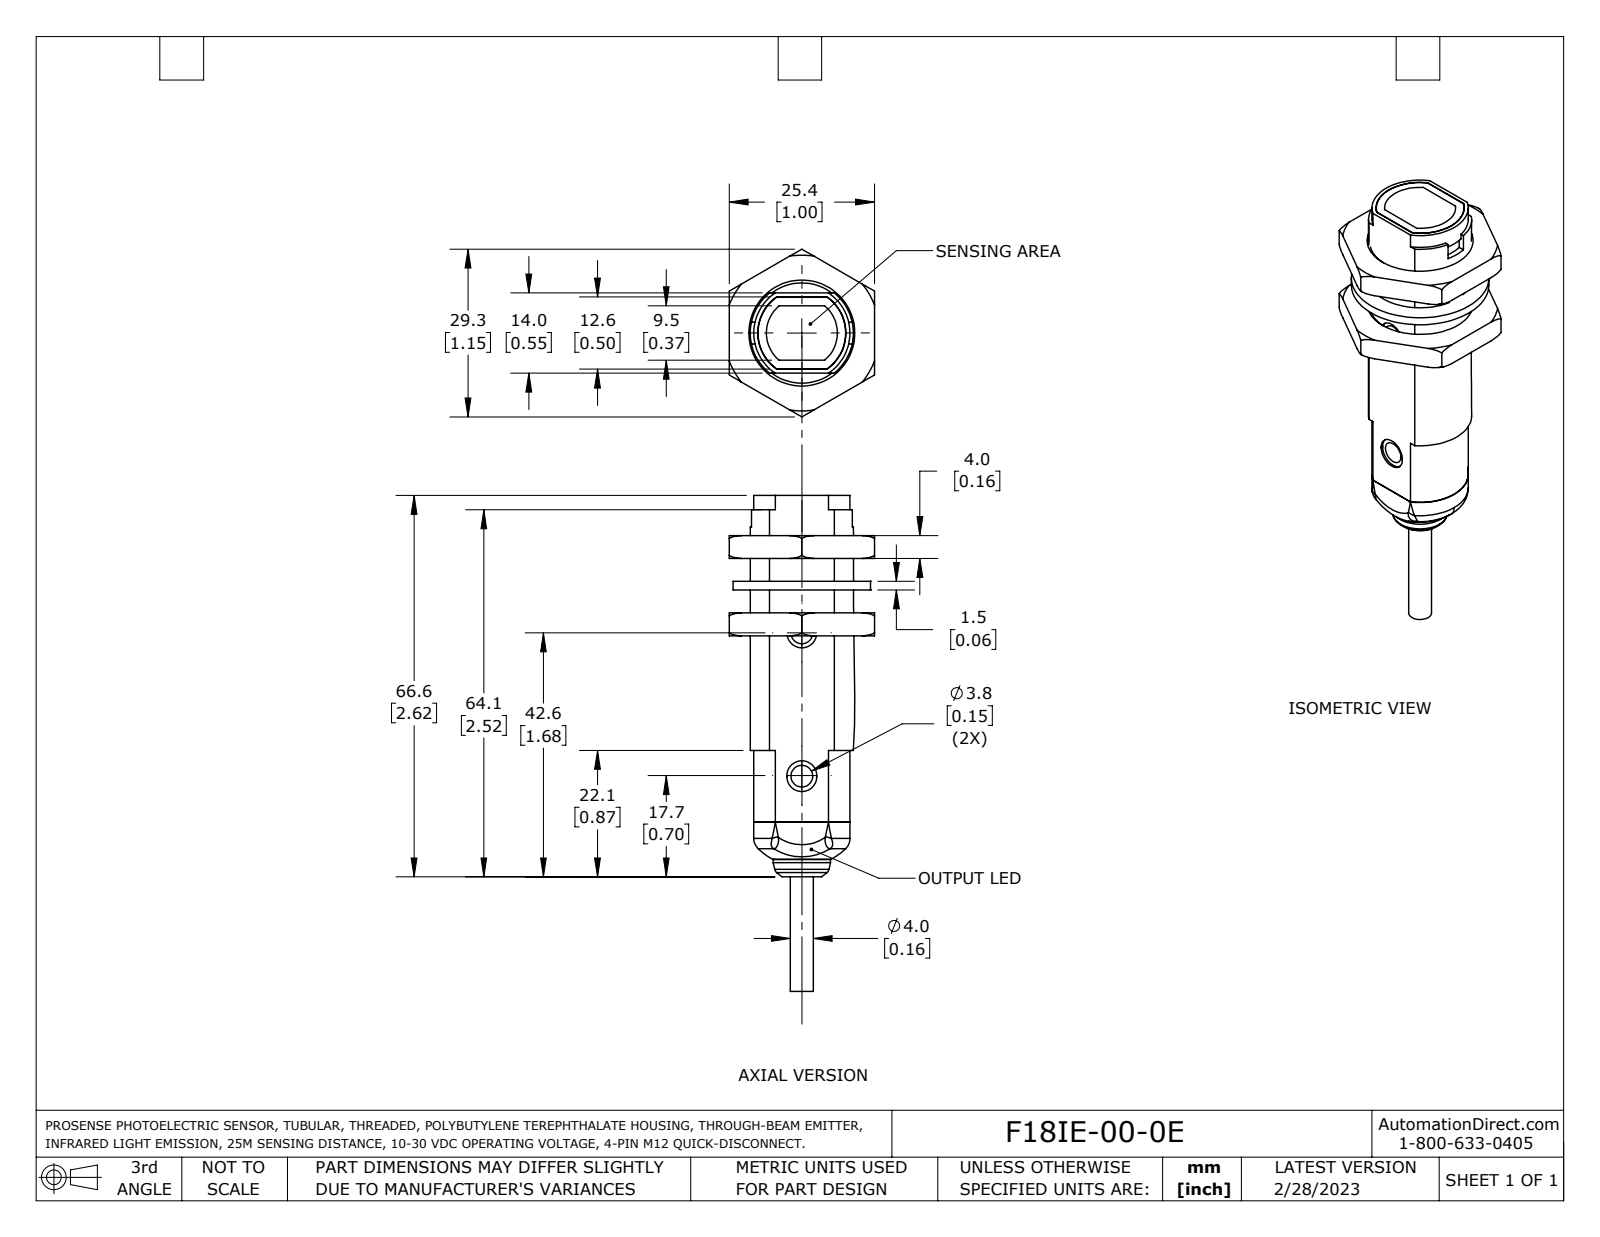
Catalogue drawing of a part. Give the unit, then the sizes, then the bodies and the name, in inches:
Units: inches
Overall size (bounding box): 2.817 × 1.153 × 0.998
Round holes (diameter × count): ⌀0.15 ×2, ⌀0.205 ×1, ⌀0.689 ×1, ⌀0.709 ×1
Round bosses / shafts (diameter × count): ⌀0.042 ×4, ⌀0.945 ×1, ⌀0.472 ×1, ⌀0.413 ×1
Partial cylindrical surfaces — rounded edges, fillets, slot ends (radius × count): R0.039 ×4, R0.059 ×4, R0.102 ×2, R1.102 ×2, R0.024 ×1, R0.301 ×1, R0.303 ×1, R0.311 ×1
Main face-to-face distances: 0.157, 0.374, 0.551, 0.531, 0.217, 0.315, 0.998, 0.689, 0.433, 0.059
Hole centre spacings: 0.984
Volume: 0.991 in³ · Surface area: 12.1 in²
Bodies: 4 solids, 177 faces (71 planar, 46 cylindrical, 60 other)
Part name (STEP PRODUCT): F18IE-00-0E
STEP written by: SolidWorks 2021 (AUTOMOTIVE_DESIGN)
